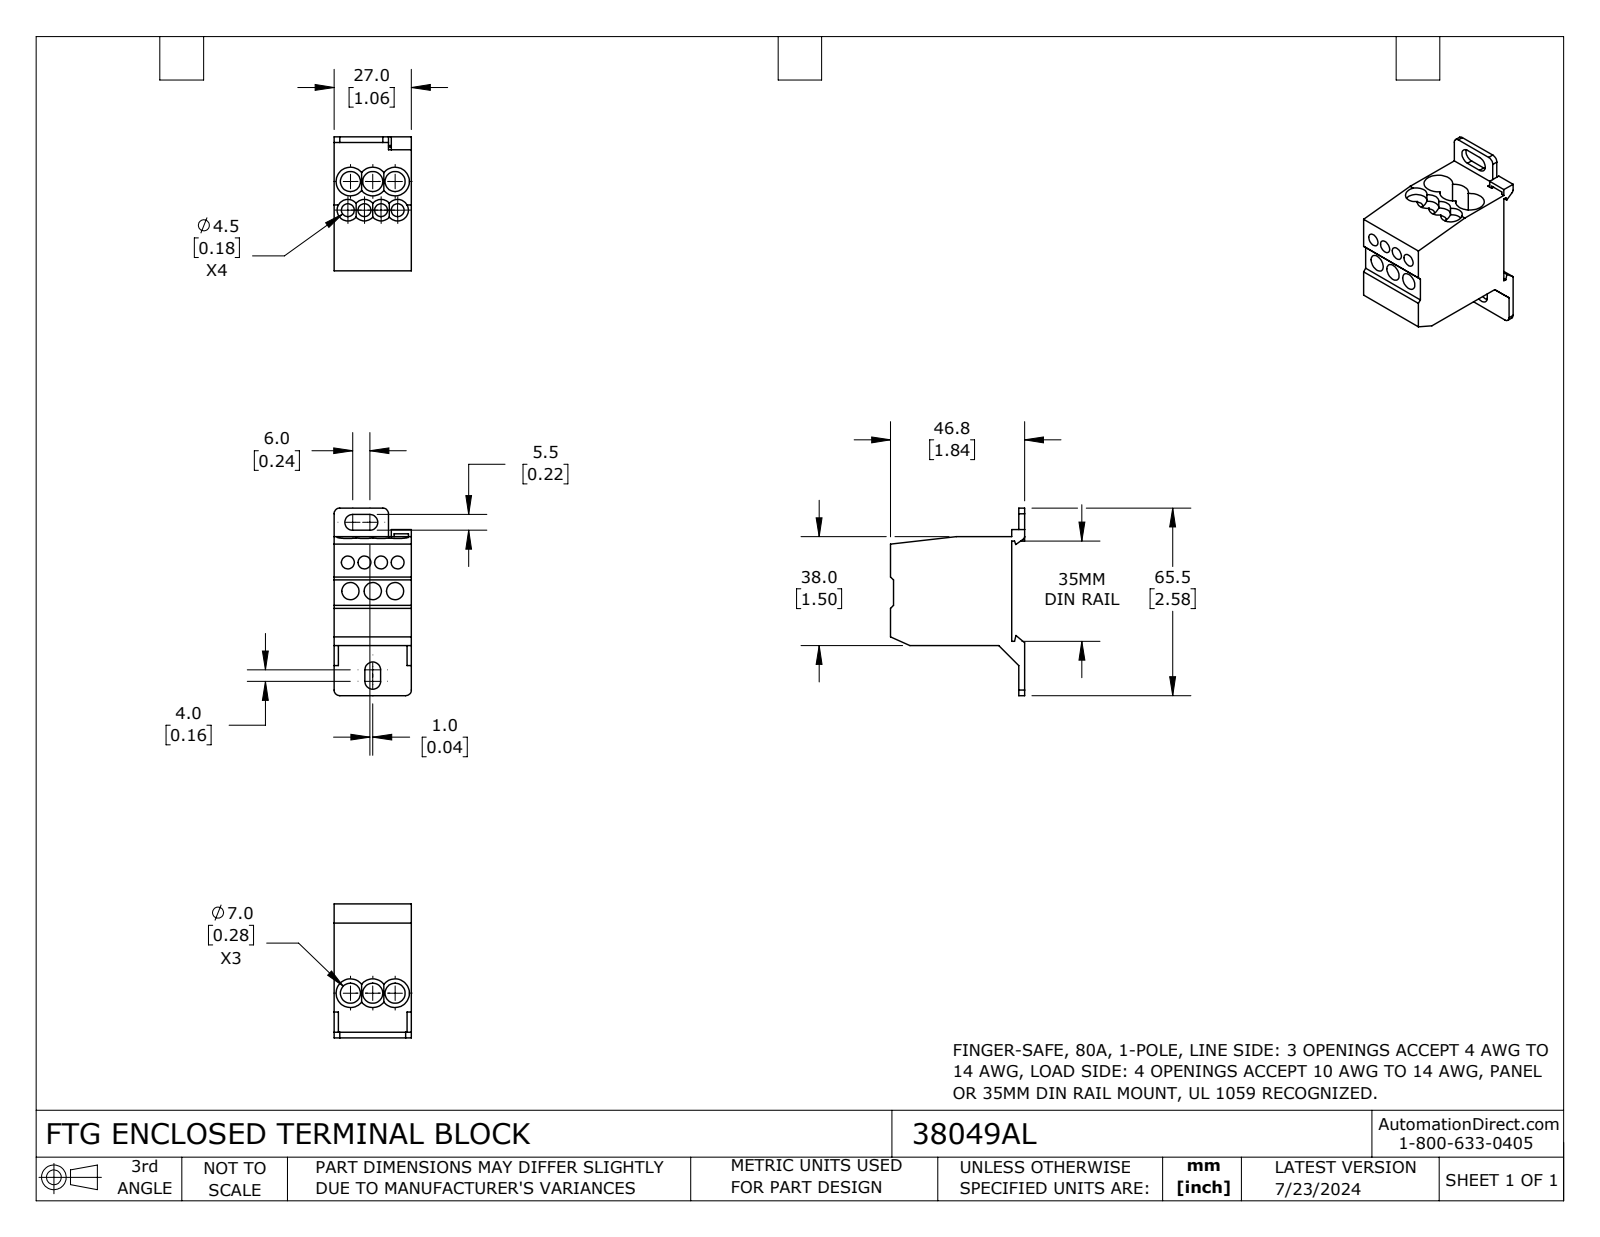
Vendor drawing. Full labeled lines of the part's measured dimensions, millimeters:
Part name (STEP PRODUCT): 38049AL
STEP written by: SolidWorks 2023 (CONFIG_CONTROL_DESIGN)
Units: millimetres
Bodies: 1 solid, 131 faces (48 planar, 55 cylindrical, 28 other)
Overall size (bounding box): 65.5 × 46.8 × 27
Volume: 34 580 mm³ · Surface area: 13 030 mm²
Round holes (diameter × count): ⌀4.5 ×8, ⌀6 ×3, ⌀7 ×3
Partial cylindrical surfaces — rounded edges, fillets, slot ends (radius × count): R2 ×4, R2.7 ×4, R3.8 ×4, R5 ×3, R1 ×1
Main face-to-face distances: 27, 4.5, 2.5, 2, 46.8, 44.8, 42.3, 38, 1, 36.5
Hole centre spacings: 5.8, 7.8, 10, 10.4, 11.2, 11.6, 13.3, 14.7
